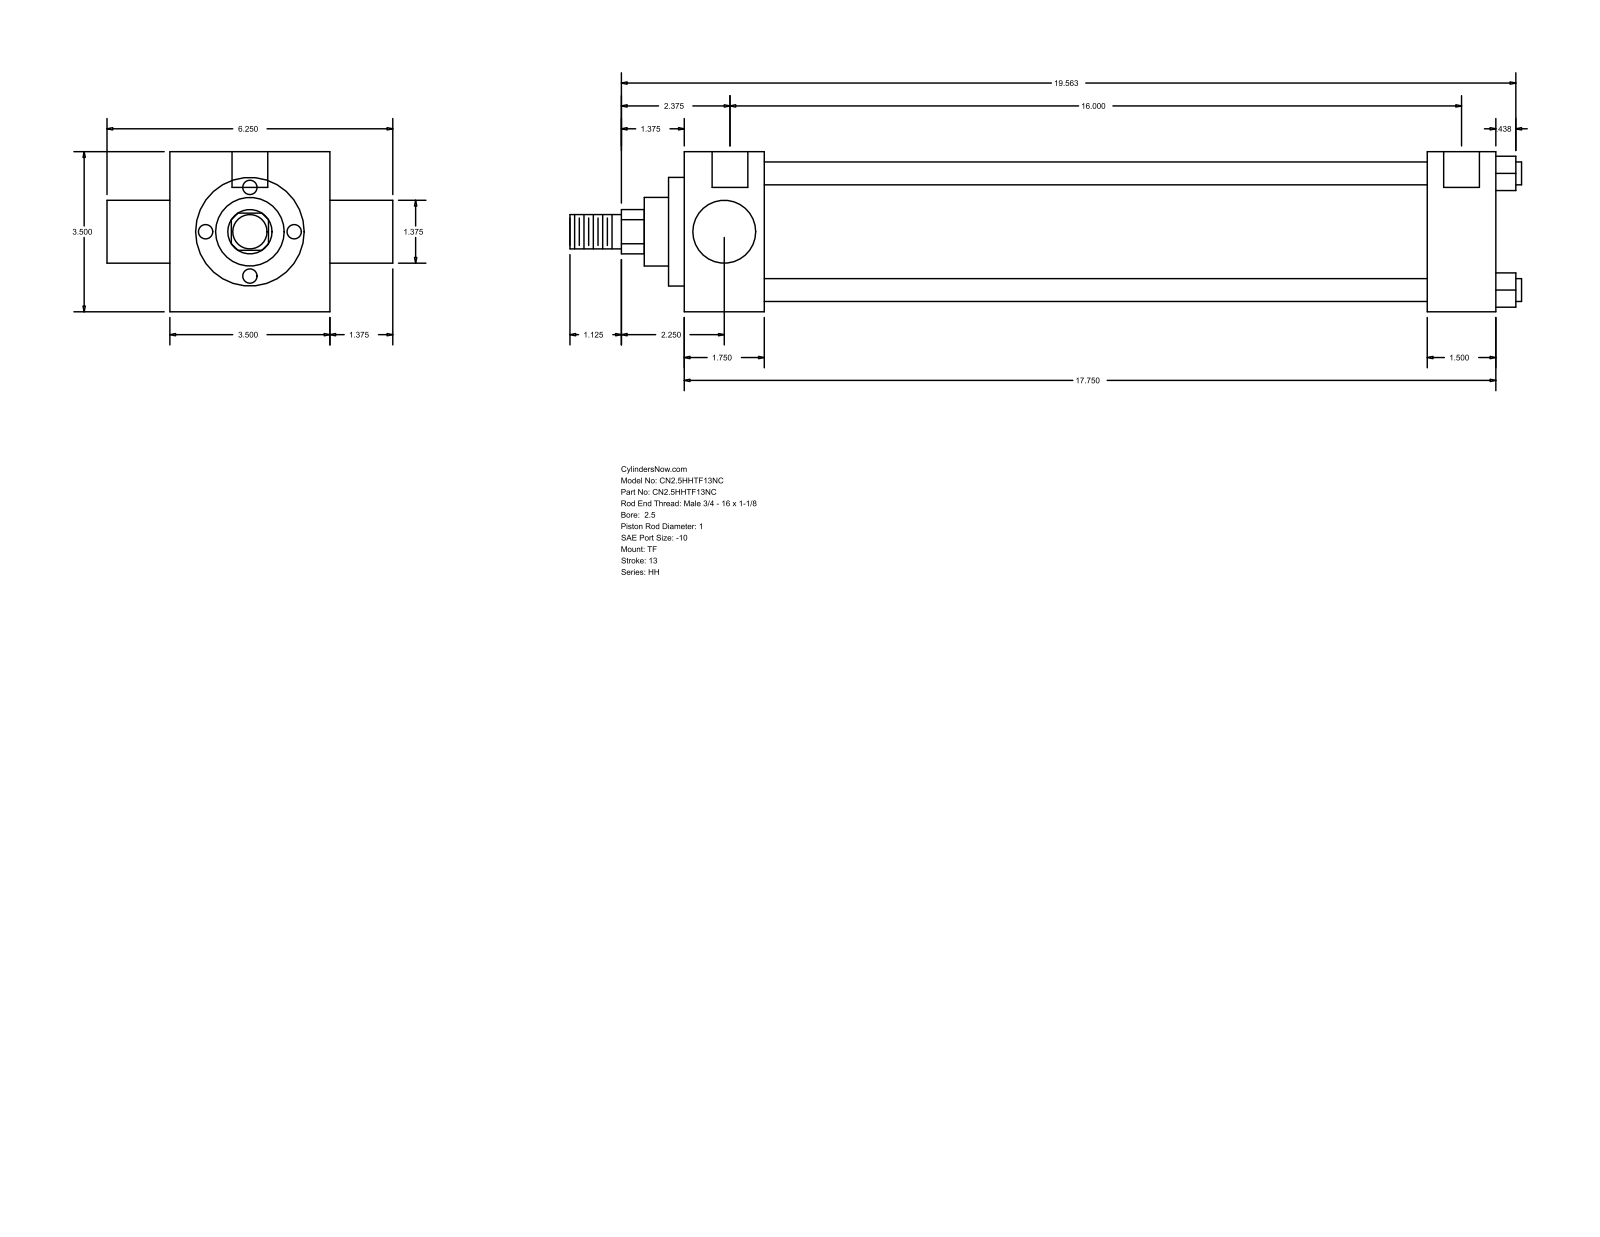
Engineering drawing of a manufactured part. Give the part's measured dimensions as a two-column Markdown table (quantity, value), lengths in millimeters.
| quantity | value |
| --- | --- |
| part name | HH_TF__0250_1 |
| STEP written by | GSSL Pune (CONFIG_CONTROL_DESIGN) |
| units | millimeters |
| bodies | 0 solids, 86 faces (61 planar, 25 cylindrical, 0 other) |
| overall size | 528.64 × 158.75 × 88.9 |
| round holes (diameter × count) | 5.56 × 3, 19.84 × 2 |
| round bosses / shafts (diameter × count) | 12.7 × 4, 73.03 × 1, 60.33 × 1, 38.1 × 1, 34.92 × 1, 25.4 × 1, 19.05 × 1 |
| partial cylindrical surfaces (radius × count) | 12.29 × 1 |
| main face-to-face distances | 88.9, 450.85, 44.46, 406.39, 412.76, 368.3, 38.09, 34.93, 123.83, 8.73 |
| hole center spacings | 1.58, 1.59, 406.4, 407.98, 407.99, 409.57 |
